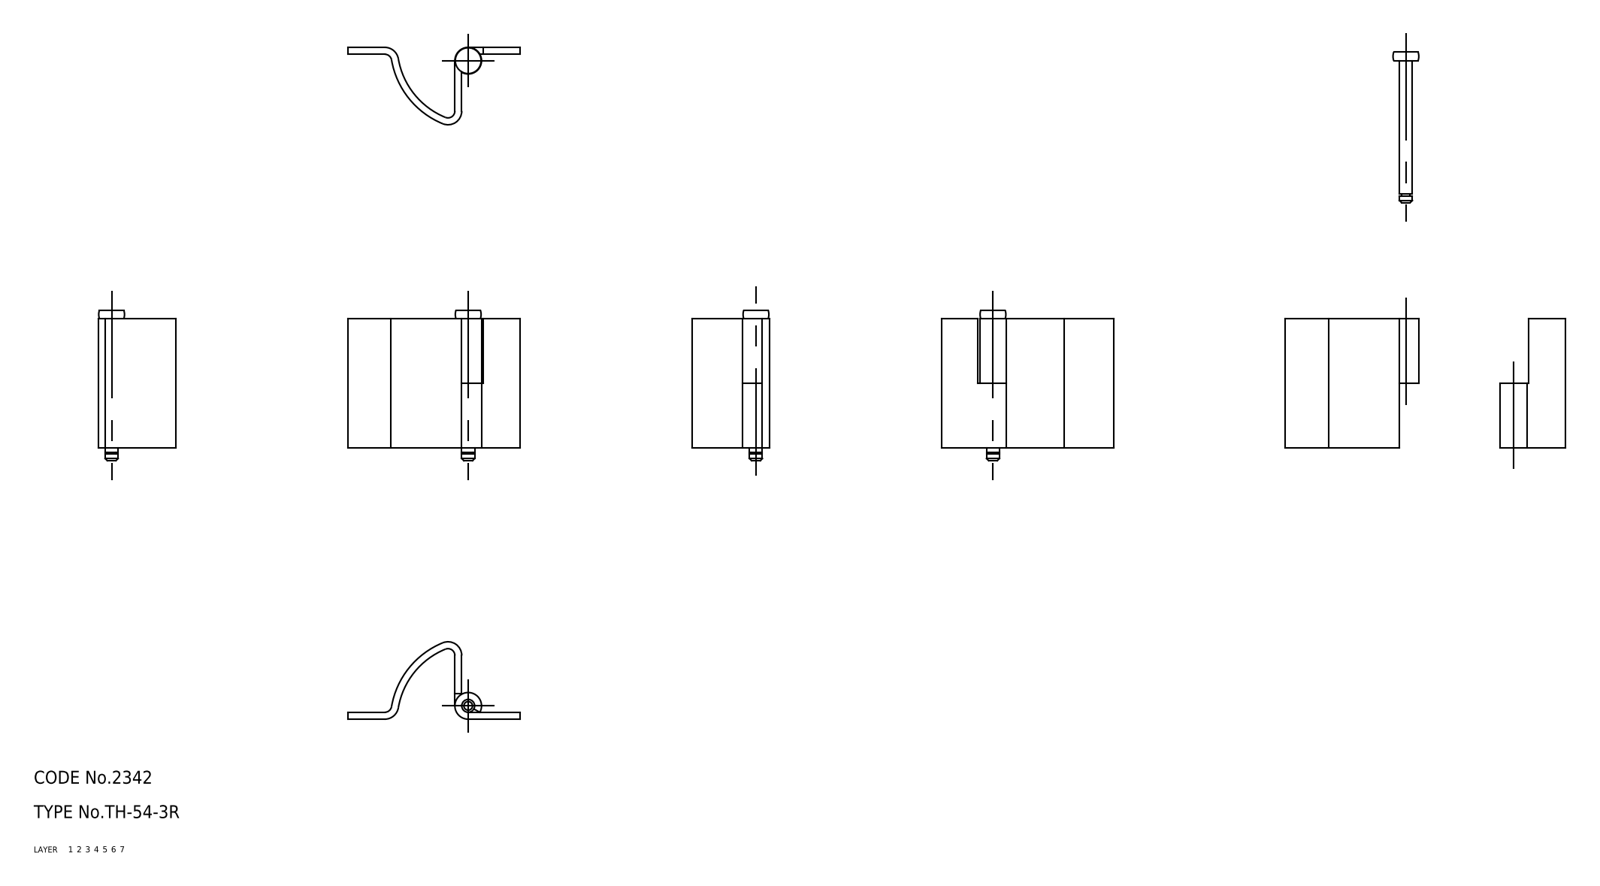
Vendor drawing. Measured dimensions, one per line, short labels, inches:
name: hinge piece_B_mr; hinge piece_A_mr; shaft; TH_54_3_R_11142_36
written by: CADfix (AUTOMOTIVE_DESIGN)
unit: in
bodies: 3 solids, 42 faces (0 planar, 0 cylindrical, 42 other)
size: 1.575 × 1.378 × 0.709
volume: 0.217 in³; area: 7.676 in²
